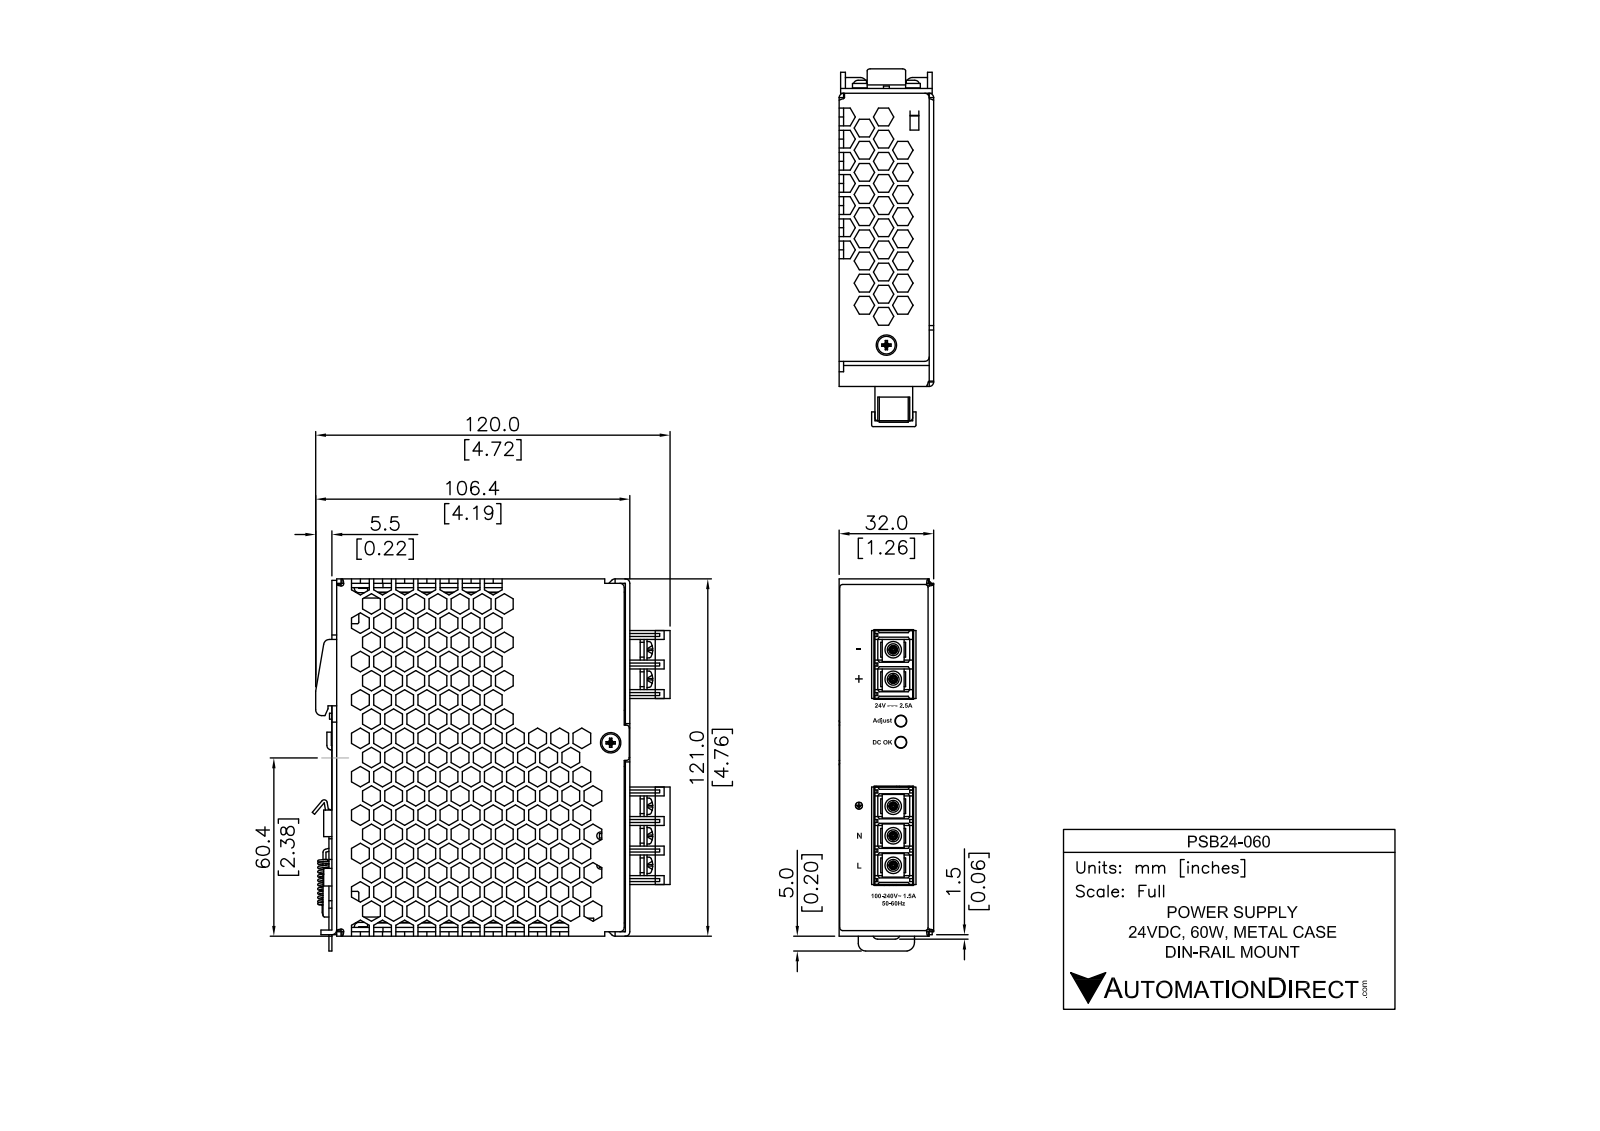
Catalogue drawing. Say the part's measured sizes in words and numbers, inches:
The part is named "PSB24-060". Its 3-D file was written by "SolidWorks 2011 (CONFIG_CONTROL_DESIGN)". It is 1 solid with 1896 faces: 1764 planar, 69 cylindrical and 63 other. Overall it measures 4.946 by 4.687 by 1.26 inches. Its volume is 5.14 cubic inches and its surface area 112.7 square inches. Round holes: 2 of diameter 0.145. Round bosses or shafts: 3 of diameter 0.205, 2 of diameter 0.23, 2 of diameter 0.125. Partial cylindrical surfaces (rounded edges, fillets, slot ends): 17 of radius 0.06, 14 of radius 0.03, 2 of radius 0.036, 2 of radius 0.04, 1 of radius 0.01, 1 of radius 0.05, 1 of radius 0.07, 1 of radius 0.079. The main face-to-face distances are 0.07, 1.188, 1.258, 1.19, 0.068, 1.12, 3.577, 0.075, 4.685, 0.3. The hole center spacings are 0.3.
